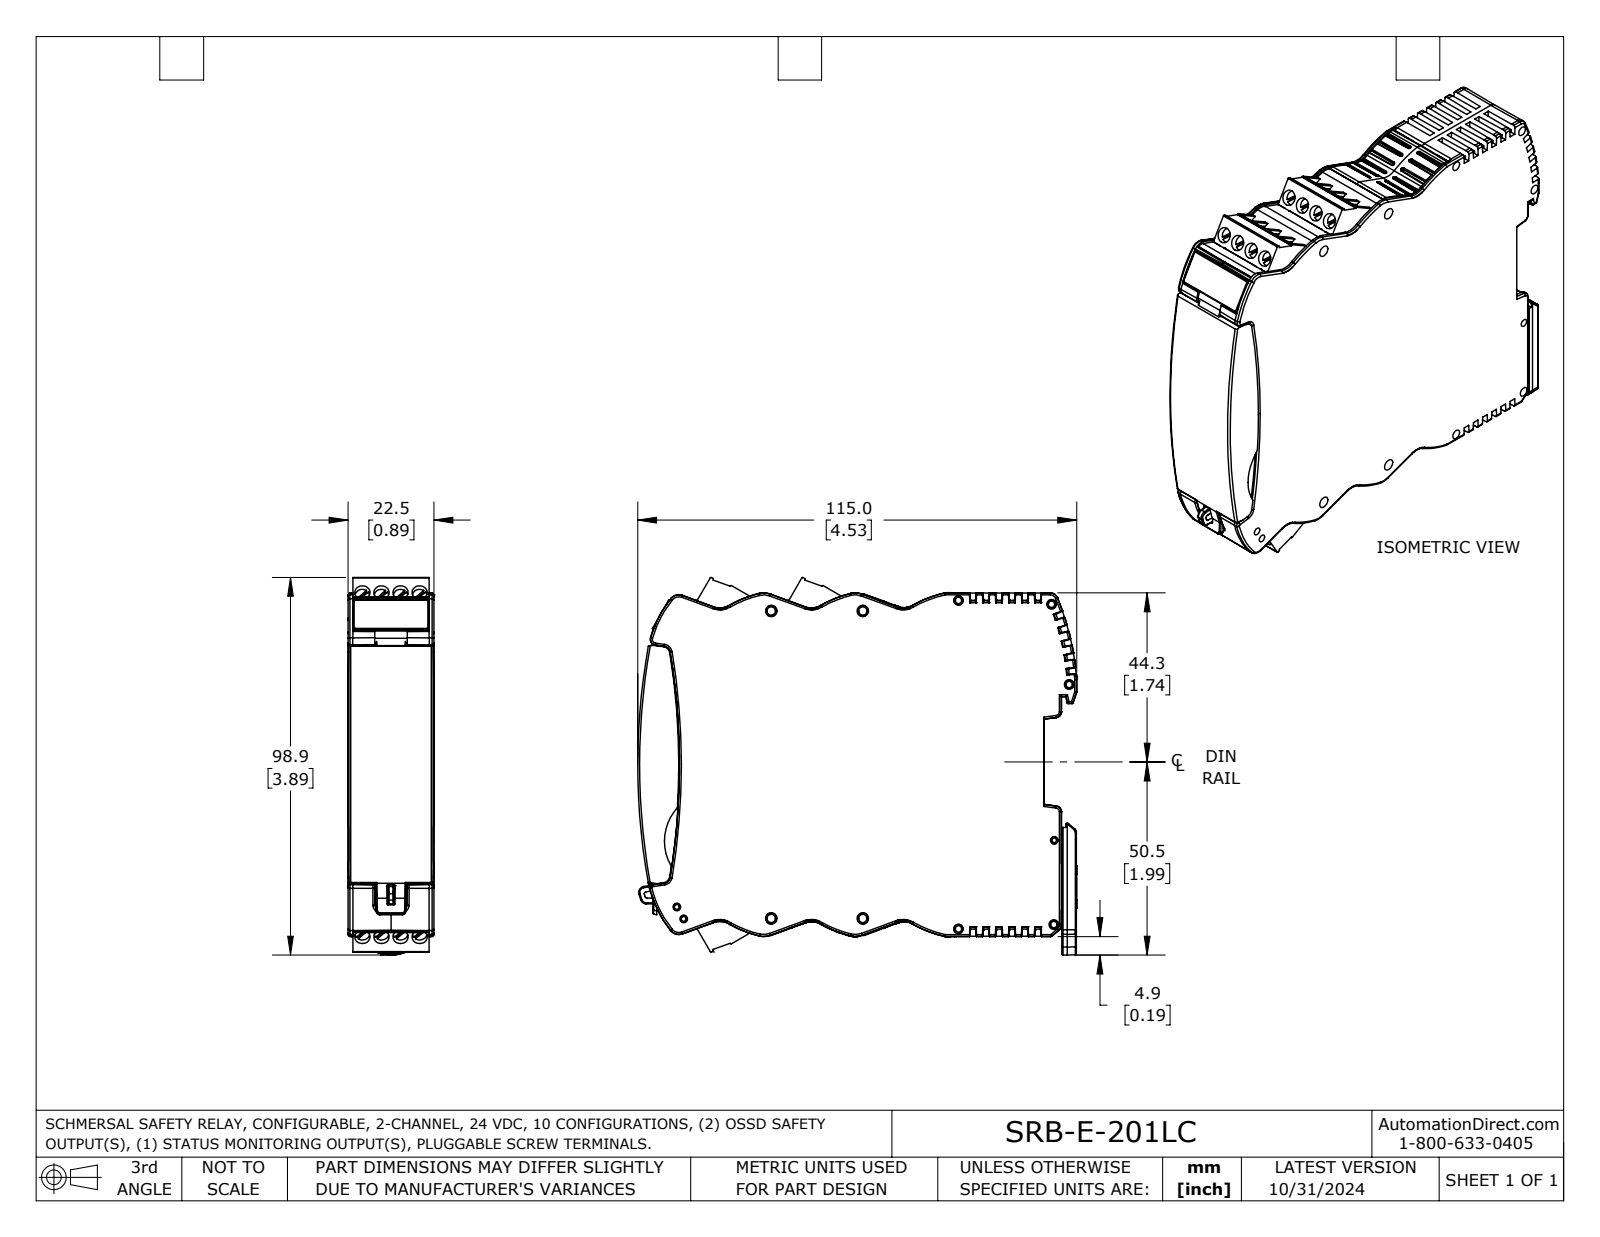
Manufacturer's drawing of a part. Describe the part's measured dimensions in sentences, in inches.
The part is named "SRB-E-201LC_REV9". Its 3-D file was written by "SolidWorks 2023 (AUTOMOTIVE_DESIGN)". It is 3 solids with 3645 faces: 1767 planar, 943 cylindrical and 935 other. Overall it measures 4.528 by 3.893 by 0.886 inches. Its volume is 12.6 cubic inches and its surface area 69.71 square inches. Round holes: 12 of diameter 0.157. Round bosses or shafts: 12 of diameter 0.149, 1 of diameter 0.067. Partial cylindrical surfaces (rounded edges, fillets, slot ends): 259 of radius 0.012, 135 of radius 0.02, 88 of radius 0.01, 77 of radius 0.008, 28 of radius 0.039, 26 of radius 0.059, 10 of radius 0.007, 9 of radius 0.03. The main face-to-face distances are 0.886, 0.059, 0.133, 0.035, 0.267, 0.041, 0.049, 0.837, 0.809, 0.134. The hole center spacings are 0.197, 0.394, 0.512, 0.472, 0.615, 0.591, 0.756.
